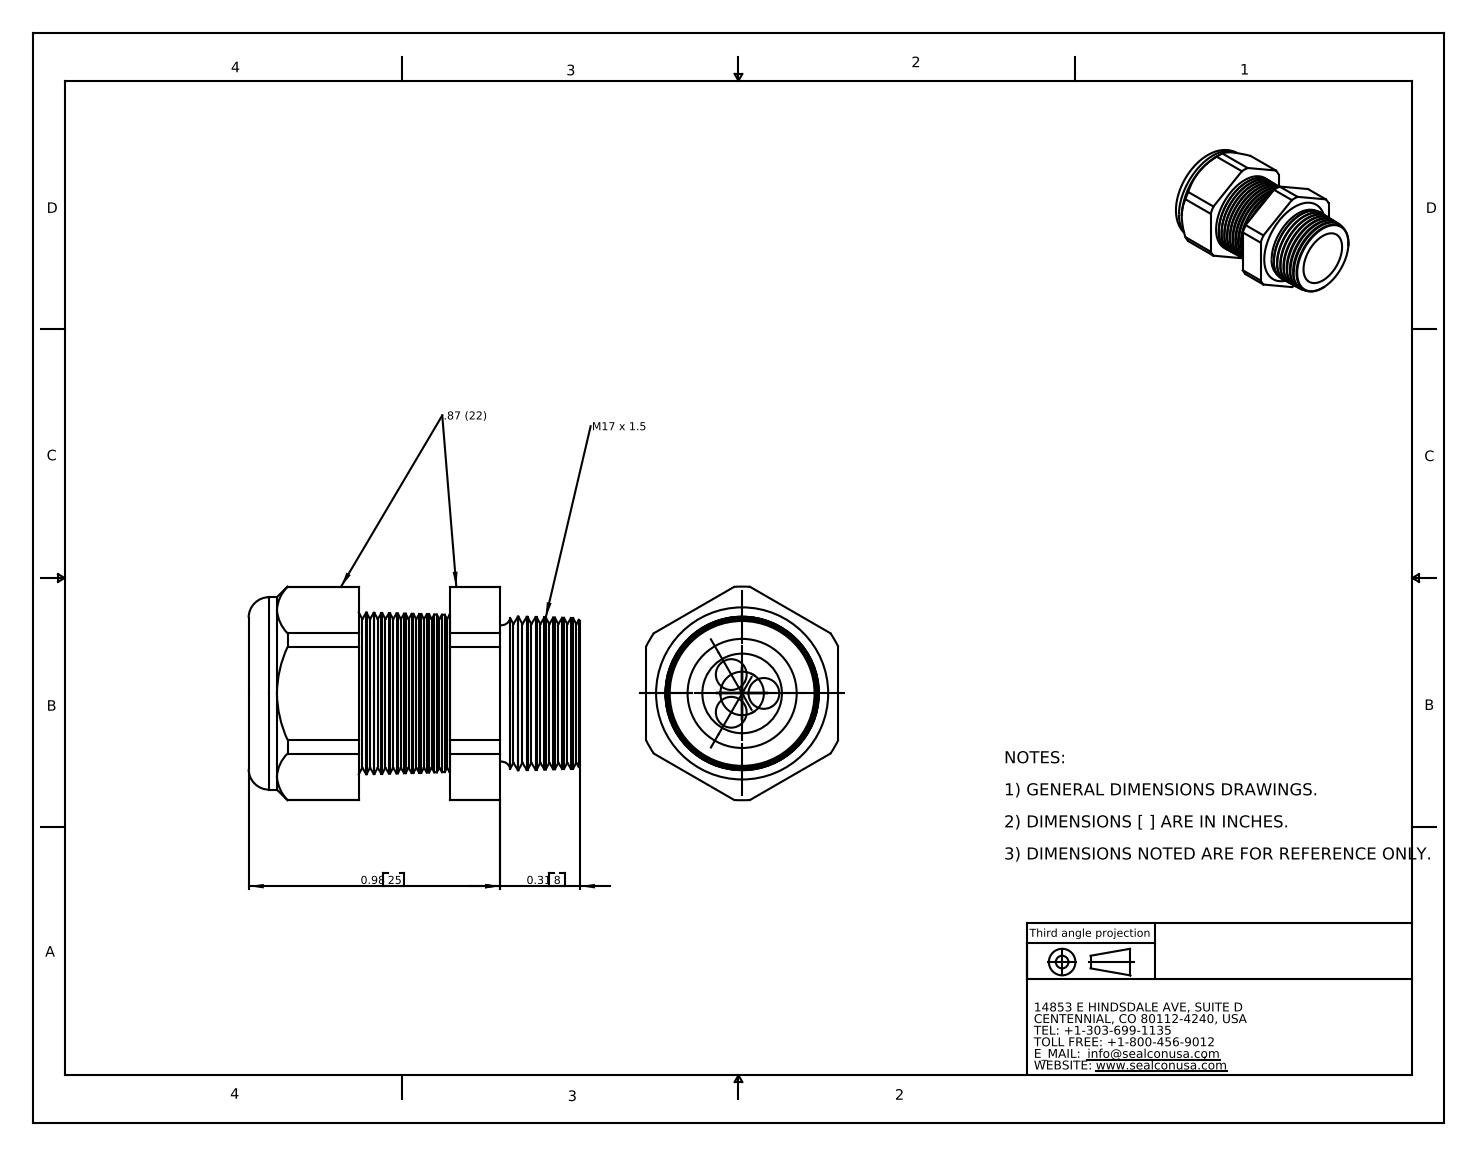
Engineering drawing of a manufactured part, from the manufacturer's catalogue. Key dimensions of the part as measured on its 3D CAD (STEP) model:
Part name (STEP PRODUCT): CD17M2-GY
STEP written by: SolidWorks 2007 (CONFIG_CONTROL_DESIGN)
Units: inches
Bodies: 2 solids, 185 faces (21 planar, 26 cylindrical, 138 other)
Overall size (bounding box): 1.29 × 0.833 × 0.75
Volume: 0.352 in³ · Surface area: 6.679 in²
Round holes (diameter × count): ⌀0.12 ×3, ⌀0.29 ×1, ⌀0.31 ×1
Round bosses / shafts (diameter × count): ⌀0.75 ×1
Partial cylindrical surfaces — rounded edges, fillets, slot ends (radius × count): R0.416 ×1
Main face-to-face distances: 0.75, 0.75, 0.783, 0.429, 0.354, 0.98, 0.551, 0.197, 1.29, 0.861
Hole centre spacings: 0.085, 0.147, 0.146
